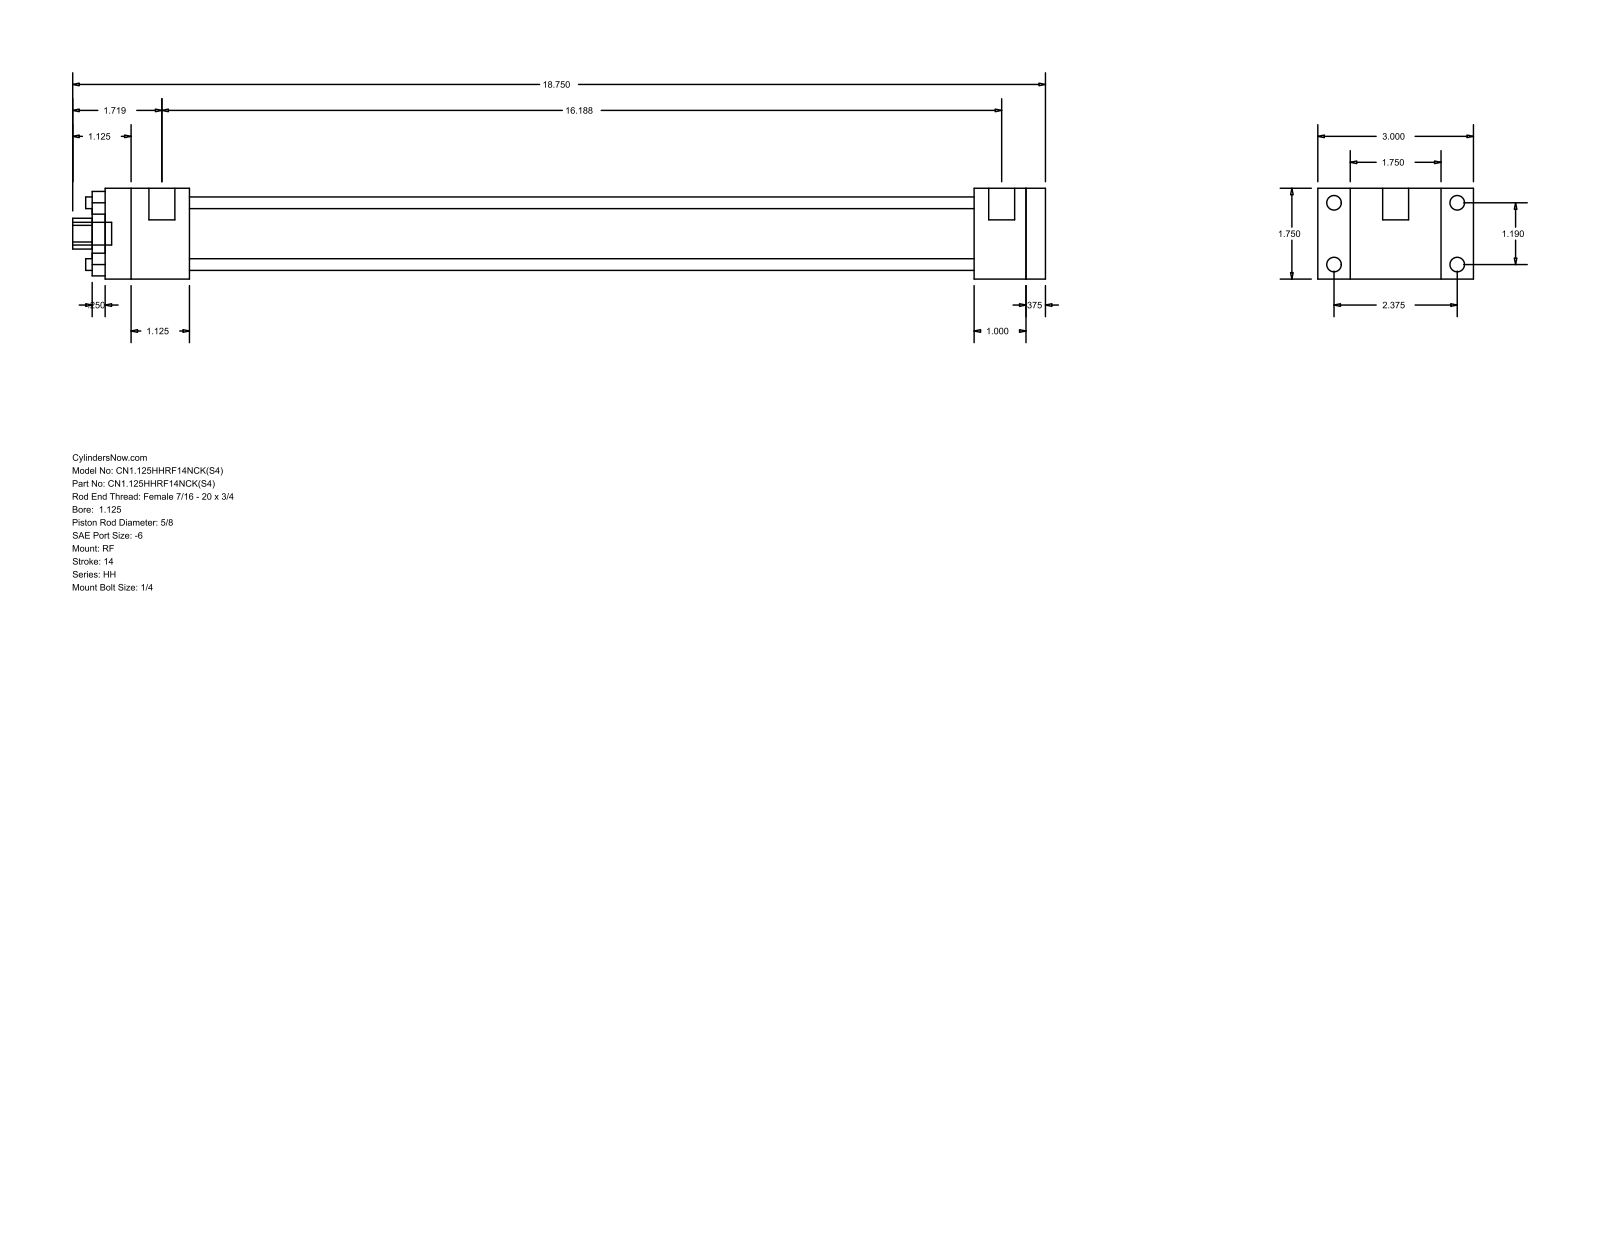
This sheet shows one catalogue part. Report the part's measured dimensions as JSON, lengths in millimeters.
{"part_name": "HH_RF__0112_0.625", "step_written_by": "GSSL Pune (CONFIG_CONTROL_DESIGN)", "units": "millimeters", "bodies": {"solids": 0, "faces": 92, "planar": 64, "cylindrical": 28, "other": 0}, "overall_size": [476.25, 76.2, 44.45], "round_holes": [[5.71, 4], [15.88, 1], [28.57, 1], [34.92, 1]], "round_bosses_or_shafts": [[7.14, 4], [5.56, 4], [12.7, 2], [11.11, 1]], "partial_cylinders_radius": [[7.54, 1]], "face_to_face_distances": [44.46, 9.52, 15.87, 409.58, 419.1, 384.17, 25.41, 34.93, 41.27, 425.44], "hole_center_spacings": [21.37, 30.22, 42.74]}
